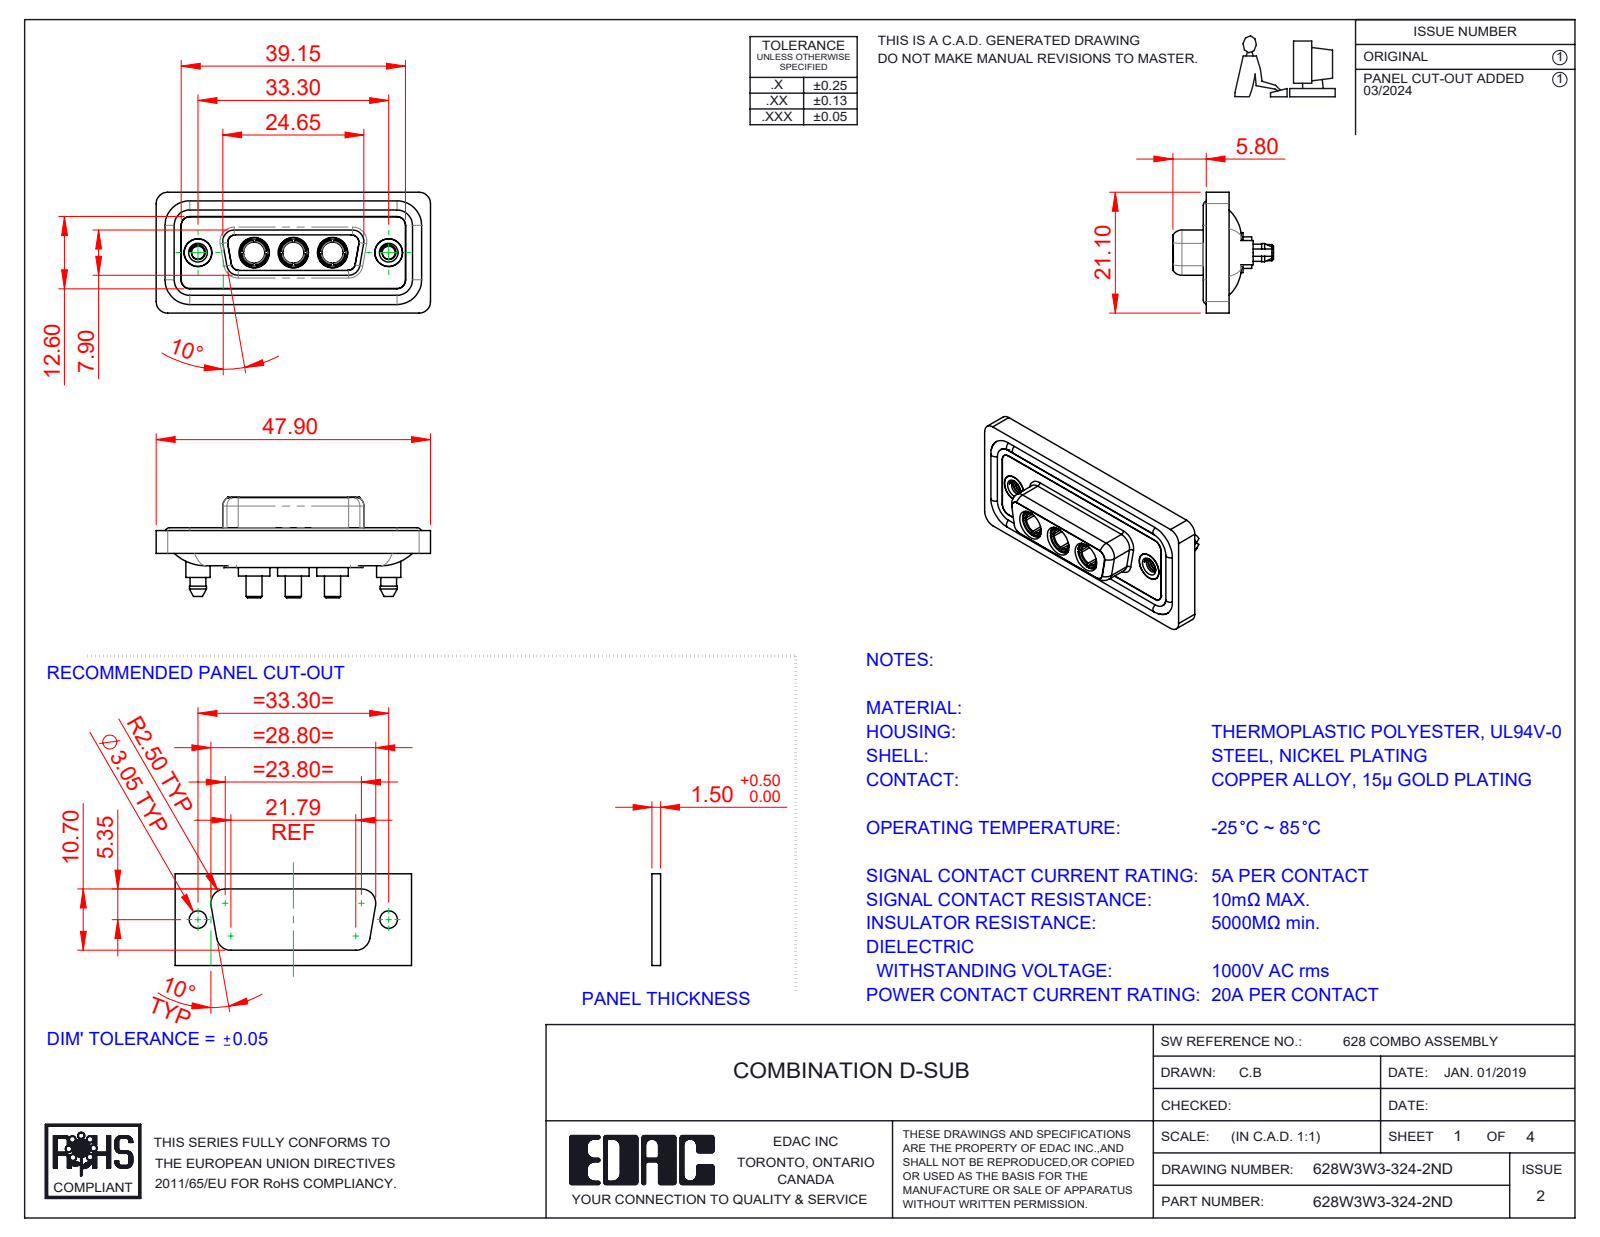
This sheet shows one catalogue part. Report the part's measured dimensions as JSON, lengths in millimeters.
{"part_name": "628Combo Waterproof Housing_15 Contacts; 628Combo Housing_3W3; Power Socket_20A S; 628Combo Shell Front_15 Contacts (+3 more)", "step_written_by": "SolidWorks 2023 (CONFIG_CONTROL_DESIGN)", "units": "millimeters", "bodies": {"solids": 13, "faces": 674, "planar": 208, "cylindrical": 305, "other": 161}, "overall_size": [47.9, 21.1, 17.55], "volume_mm3": 6162, "surface_area_mm2": 10078, "round_holes": [[4.85, 5], [3.7, 3], [5.3, 3], [2.26, 2], [4, 2], [4.05, 2], [5, 2]], "round_bosses_or_shafts": [[1.6, 4], [5.5, 3], [5.2, 3], [4.96, 3], [4.75, 3], [3.75, 3], [2.8, 3], [5.4, 2]], "partial_cylinders_radius": [[1.5, 24], [2, 20], [1.35, 12], [1.6, 10], [0.25, 4], [0.5, 4], [0.6, 4], [0.65, 4]], "face_to_face_distances": [0.4, 1.8, 1.6, 0.5, 7.45, 1.1, 2.9, 5.65, 7.05, 6.6], "hole_center_spacings": [6.85, 9.8, 16.65, 23.5, 13.7, 33.3]}
